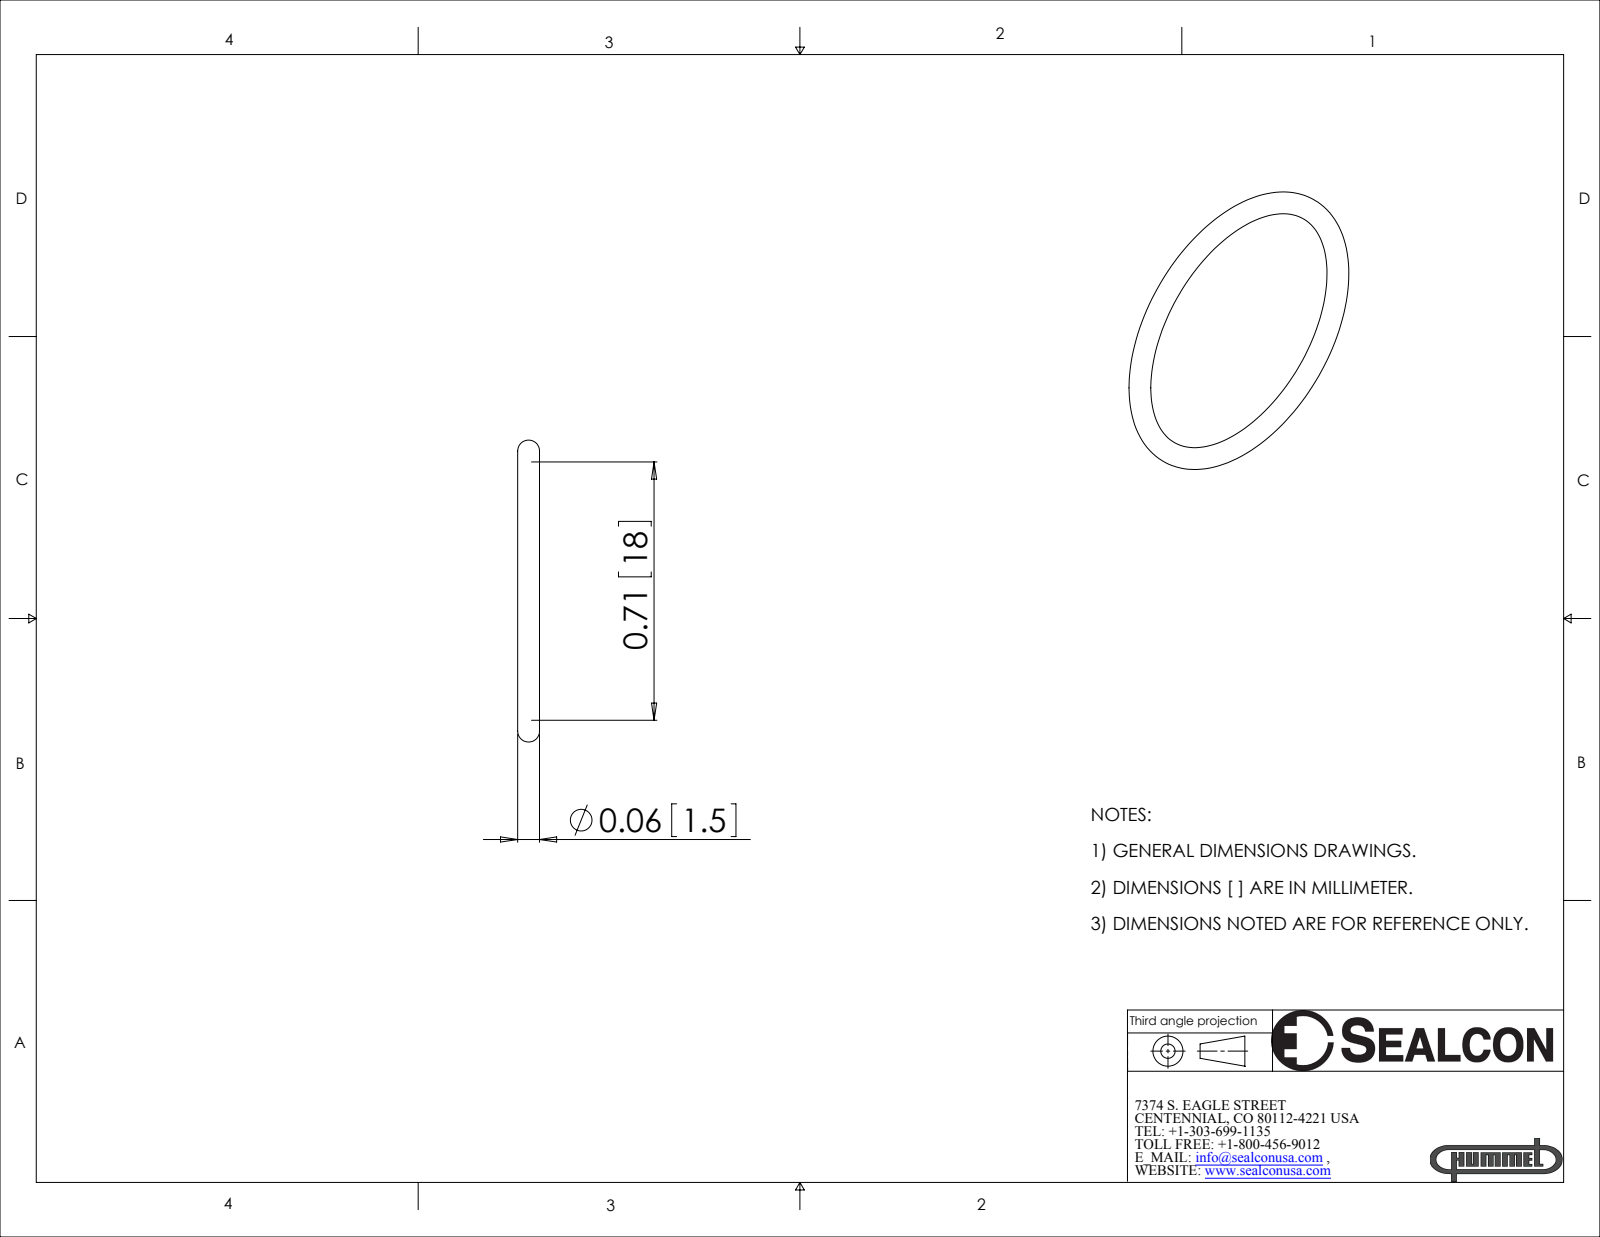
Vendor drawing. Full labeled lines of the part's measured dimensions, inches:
Part name (STEP PRODUCT): OR-16-SI
STEP written by: SolidWorks 2008 (CONFIG_CONTROL_DESIGN)
Units: inches
Bodies: 1 solid, 4 faces (0 planar, 0 cylindrical, 4 other)
Overall size (bounding box): 0.83 × 0.83 × 0.06
Volume: 0.007 in³ · Surface area: 0.456 in²
